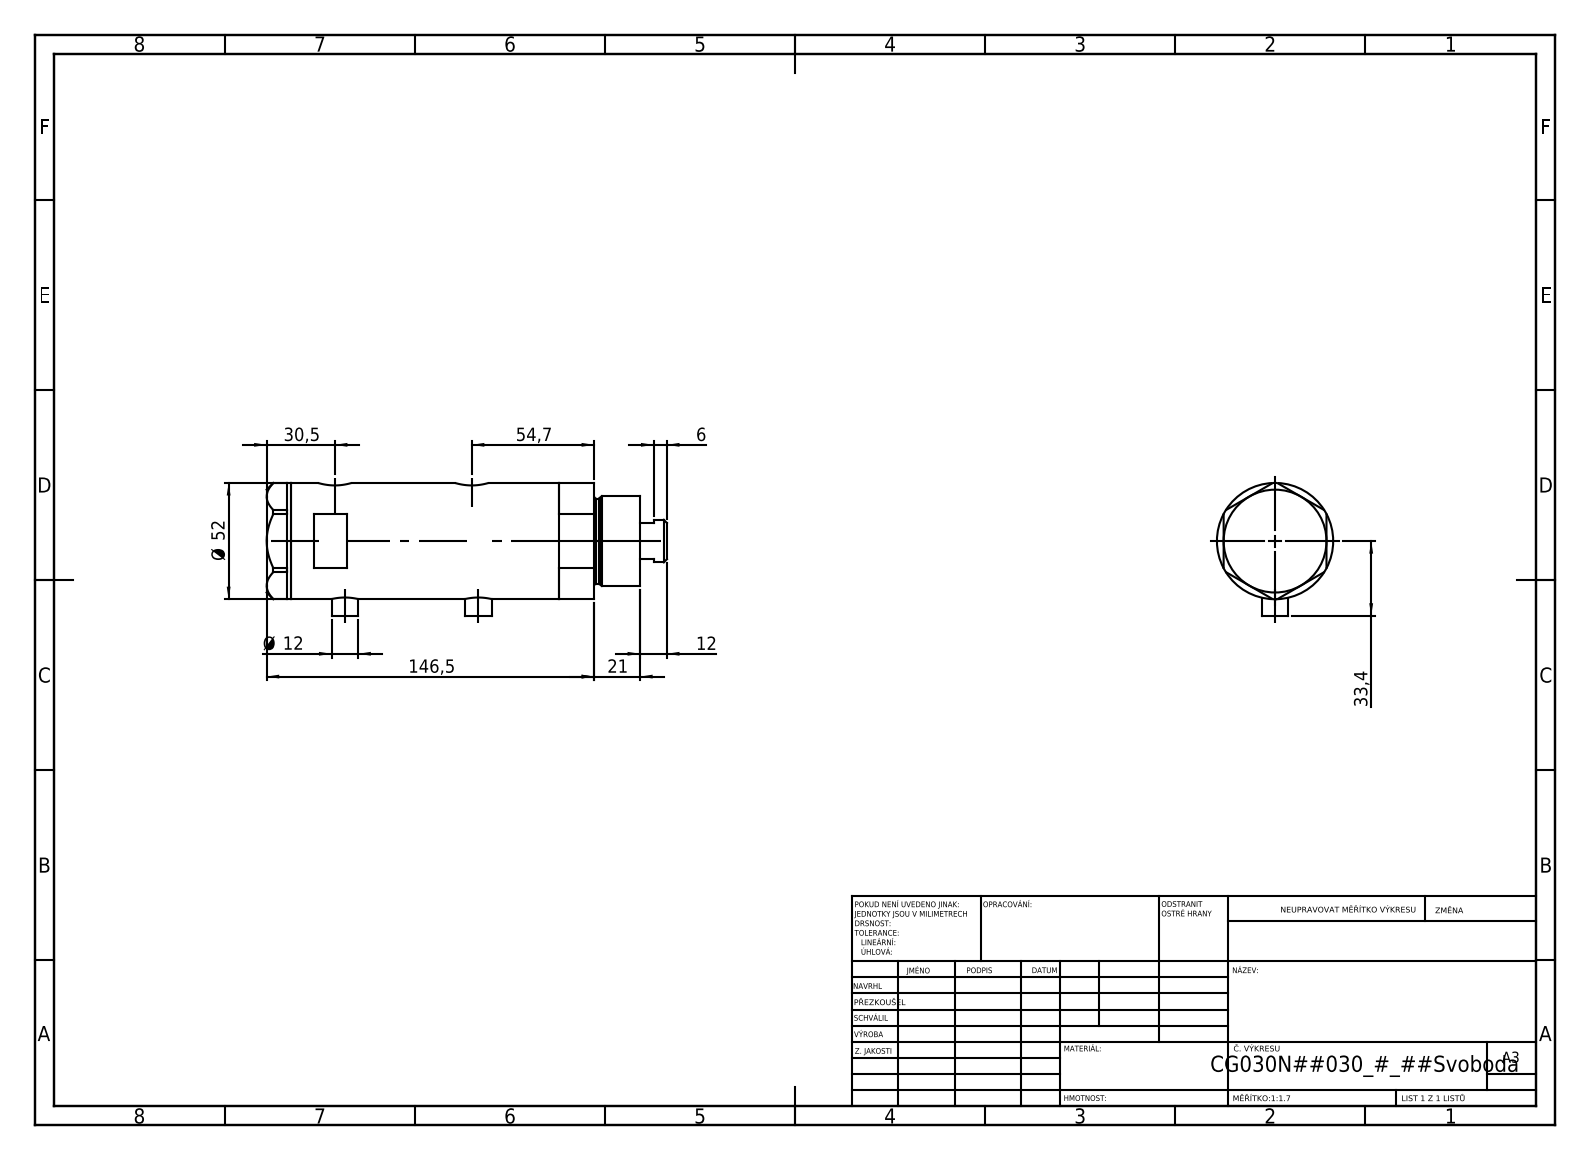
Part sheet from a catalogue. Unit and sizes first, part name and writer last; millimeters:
Units: millimetres
Overall size (bounding box): 179.02 × 59.4 × 52
Round holes (diameter × count): ⌀5 ×2, ⌀9.73 ×2, ⌀12.5 ×2, ⌀15 ×2, ⌀6.5 ×1, ⌀20 ×1, ⌀21.5 ×1, ⌀30 ×1, ⌀33 ×1, ⌀44 ×1
Round bosses / shafts (diameter × count): ⌀12 ×2, ⌀52 ×1, ⌀40 ×1, ⌀38 ×1, ⌀19 ×1
Main face-to-face distances: 23.81, 10.99, 34.8, 46, 94.55, 83.56, 59.75, 130.95, 119.96, 96.15
Hole centre spacings: 2.9, 4.5, 56.75, 59.65, 61.25, 64.15, 2.89, 2.91
Volume: 320 627 mm³ · Surface area: 75 376 mm²
Bodies: 4 solids, 140 faces (67 planar, 53 cylindrical, 20 other)
Part name (STEP PRODUCT): V270CG_FRONT; V270CG_MIDDLE; V270CG_VC; V270CG_BACK
STEP written by: SolidWorks 2019 (CONFIG_CONTROL_DESIGN)
